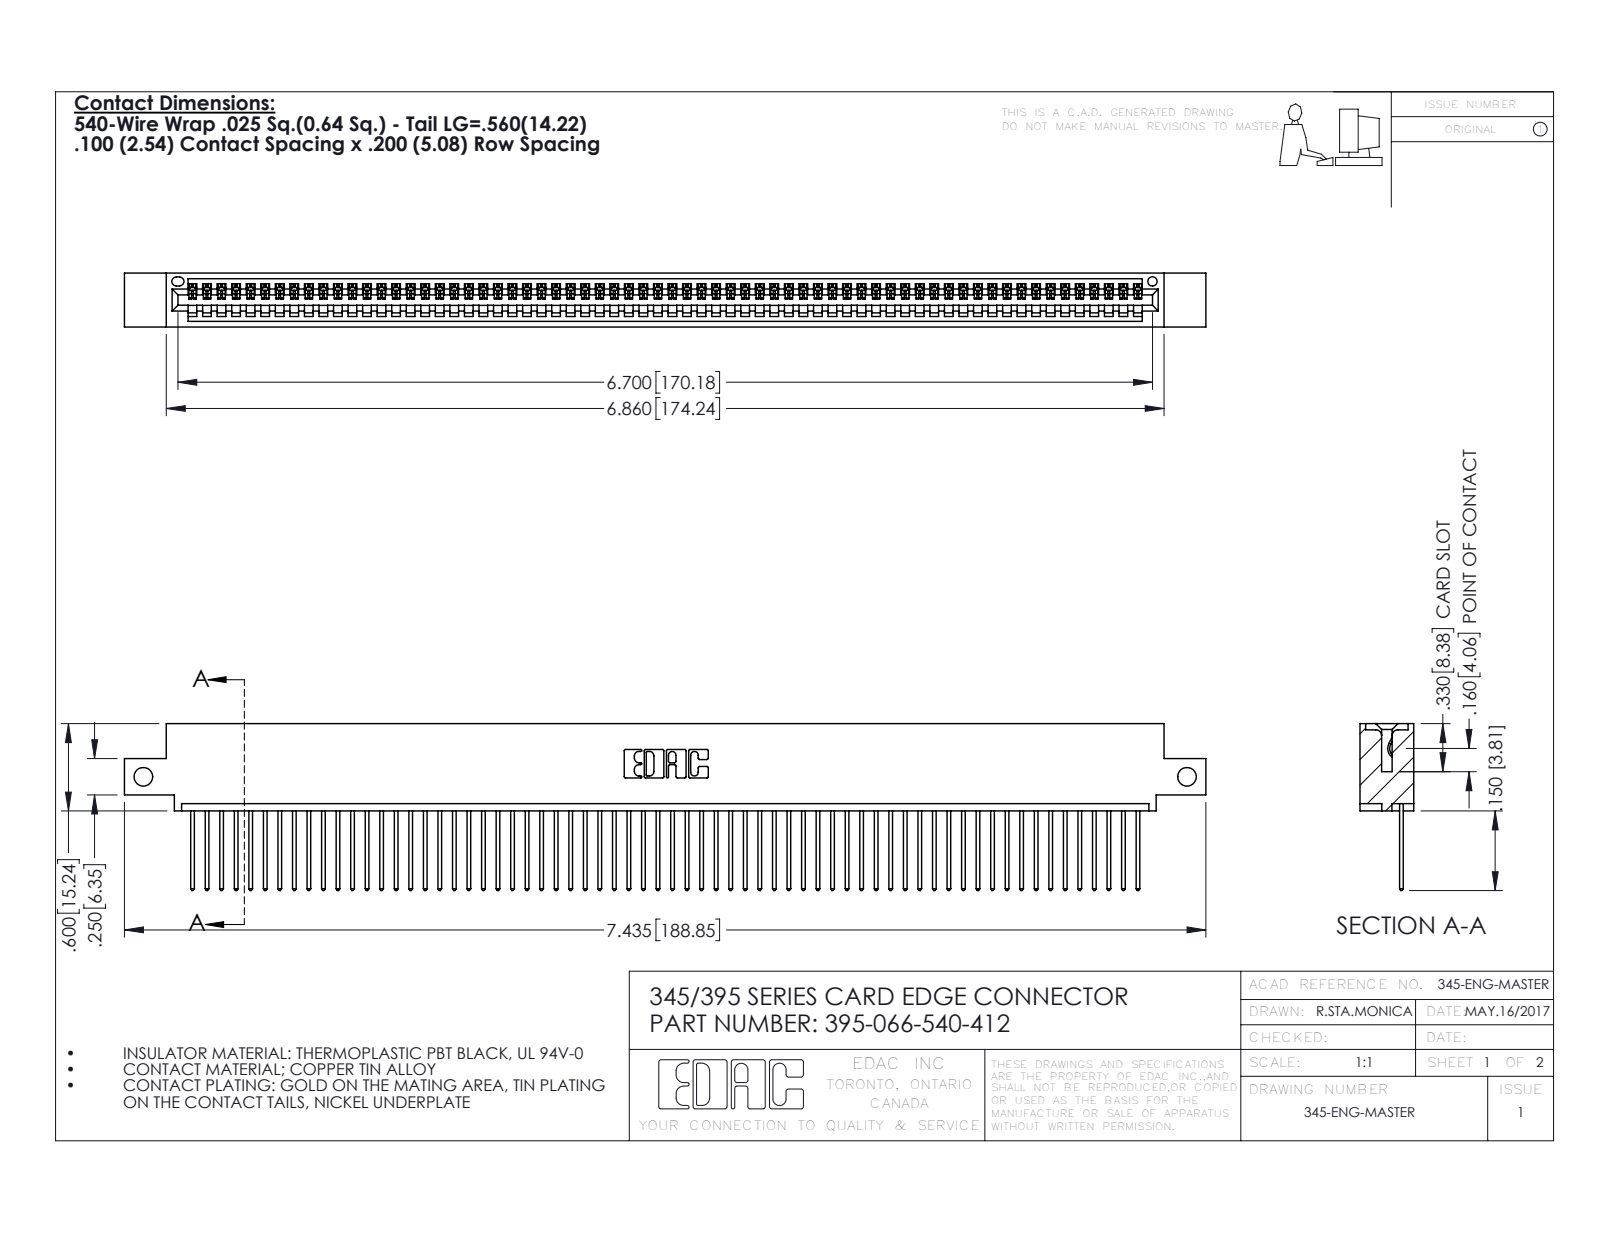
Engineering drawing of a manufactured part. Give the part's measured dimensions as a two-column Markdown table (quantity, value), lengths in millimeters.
| quantity | value |
| --- | --- |
| part name | 345-292-001_345-293-140; 345 Part_0.110 Offset - Side Mount; 395-066-540-412 |
| STEP written by | SolidWorks 2016 (CONFIG_CONTROL_DESIGN) |
| units | millimeters |
| bodies | 67 solids, 3958 faces (2724 planar, 1234 cylindrical, 0 other) |
| overall size | 188.8 × 29.1 × 9.4 |
| volume | 18 060 mm³ |
| surface area | 24 910 mm² |
| round holes (diameter × count) | 3.3 × 2, 1.6 × 1 |
| partial cylindrical surfaces (radius × count) | 0.2 × 132, 0.3 × 132, 0.3 × 22, 0.2 × 6, 0.8 × 6, 0.7 × 3, 0.8 × 2, 1 × 2 |
| main face-to-face distances | 1.8, 7.6, 9.4, 2.5, 6.9, 0.6, 5.1, 5.7, 3.8, 1.8 |
| hole center spacings | 182.2 |
